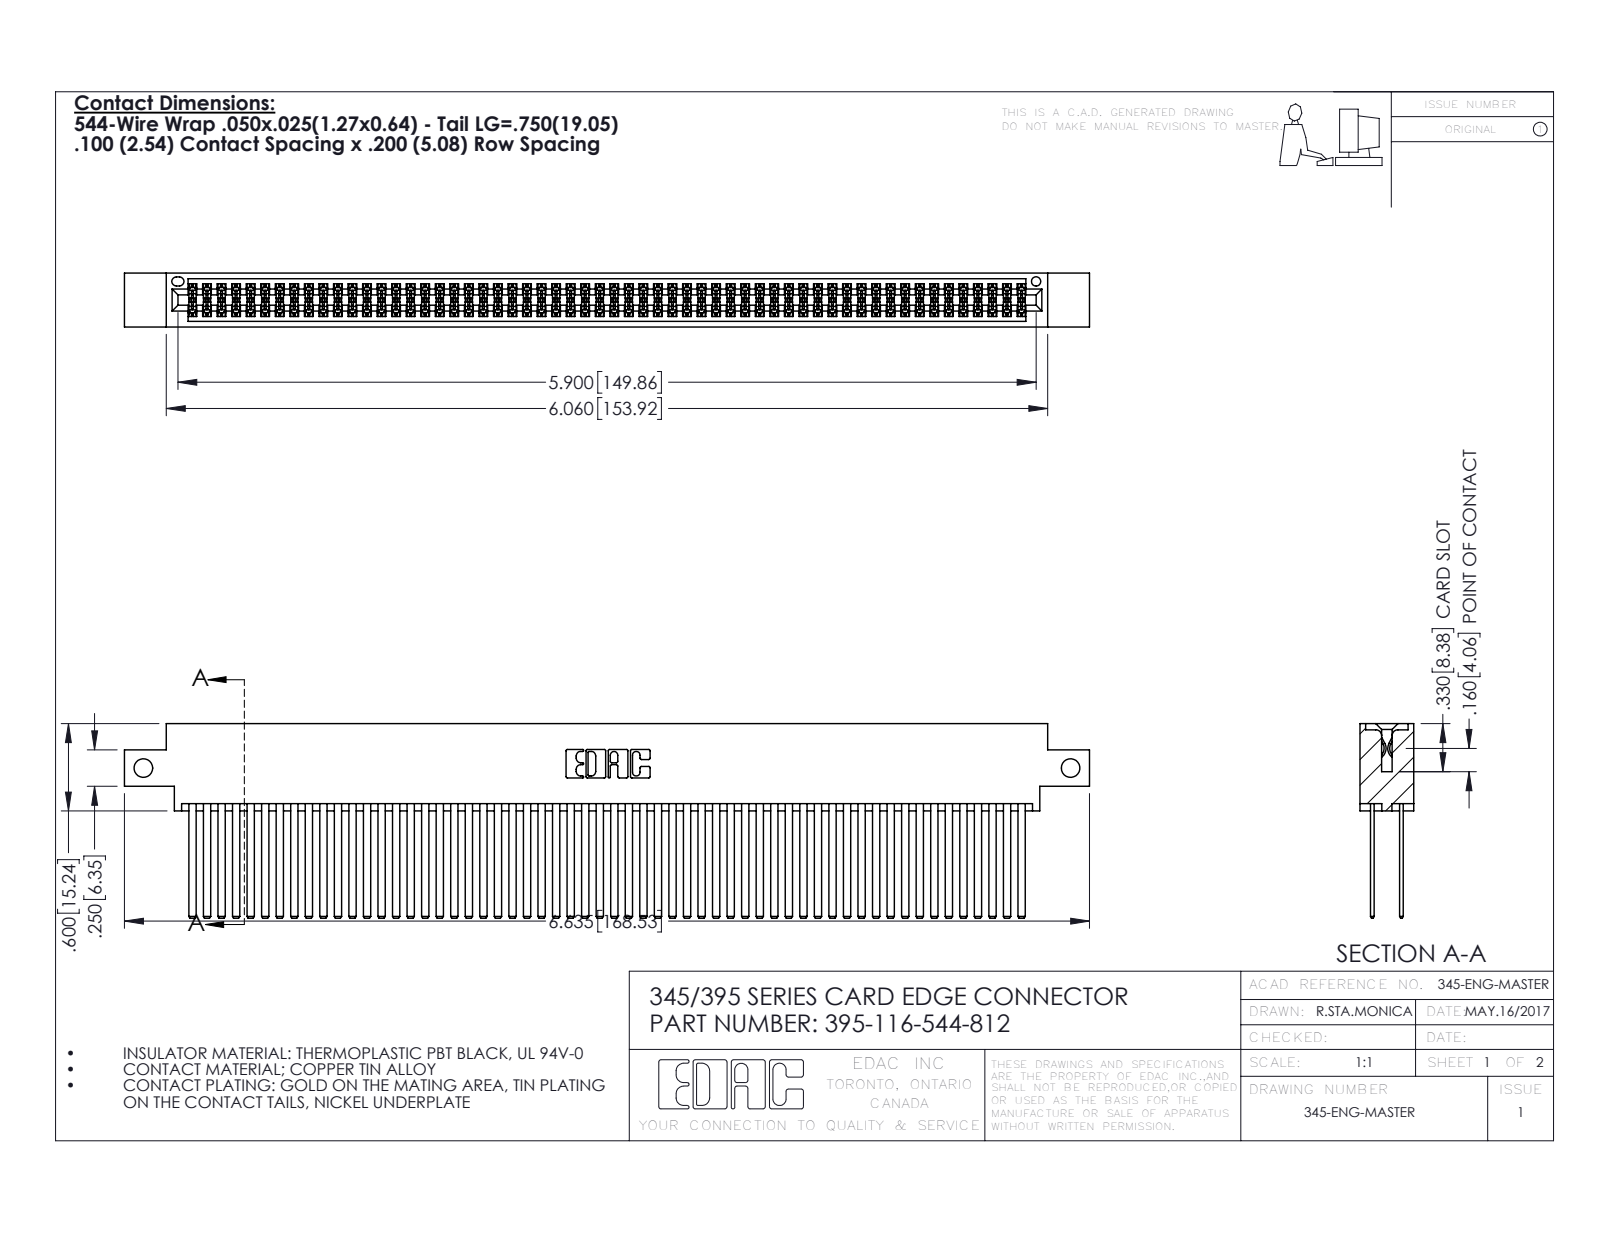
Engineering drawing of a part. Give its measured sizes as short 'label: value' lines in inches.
name: 395-116-544-812; 345-292-001_345-293-144; 345 Part_0.170 Offset - Side Mount
written by: SolidWorks 2016 (CONFIG_CONTROL_DESIGN)
unit: in
bodies: 117 solids, 5234 faces (3448 planar, 1786 cylindrical, 0 other)
size: 6.635 × 1.337 × 0.37
volume: 1.095 in³; area: 48.99 in²
holes: 2× ⌀0.128, 1× ⌀0.064
rounds: 174× R0.006, 22× R0.01, 6× R0.007, 6× R0.031, 3× R0.026, 2× R0.014, 2× R0.019, 2× R0.022
face distances: 0.2, 0.025, 0.298, 0.072, 0.098, 0.272, 0.225, 0.175, 0.37, 0.15
hole spacings: 6.375
